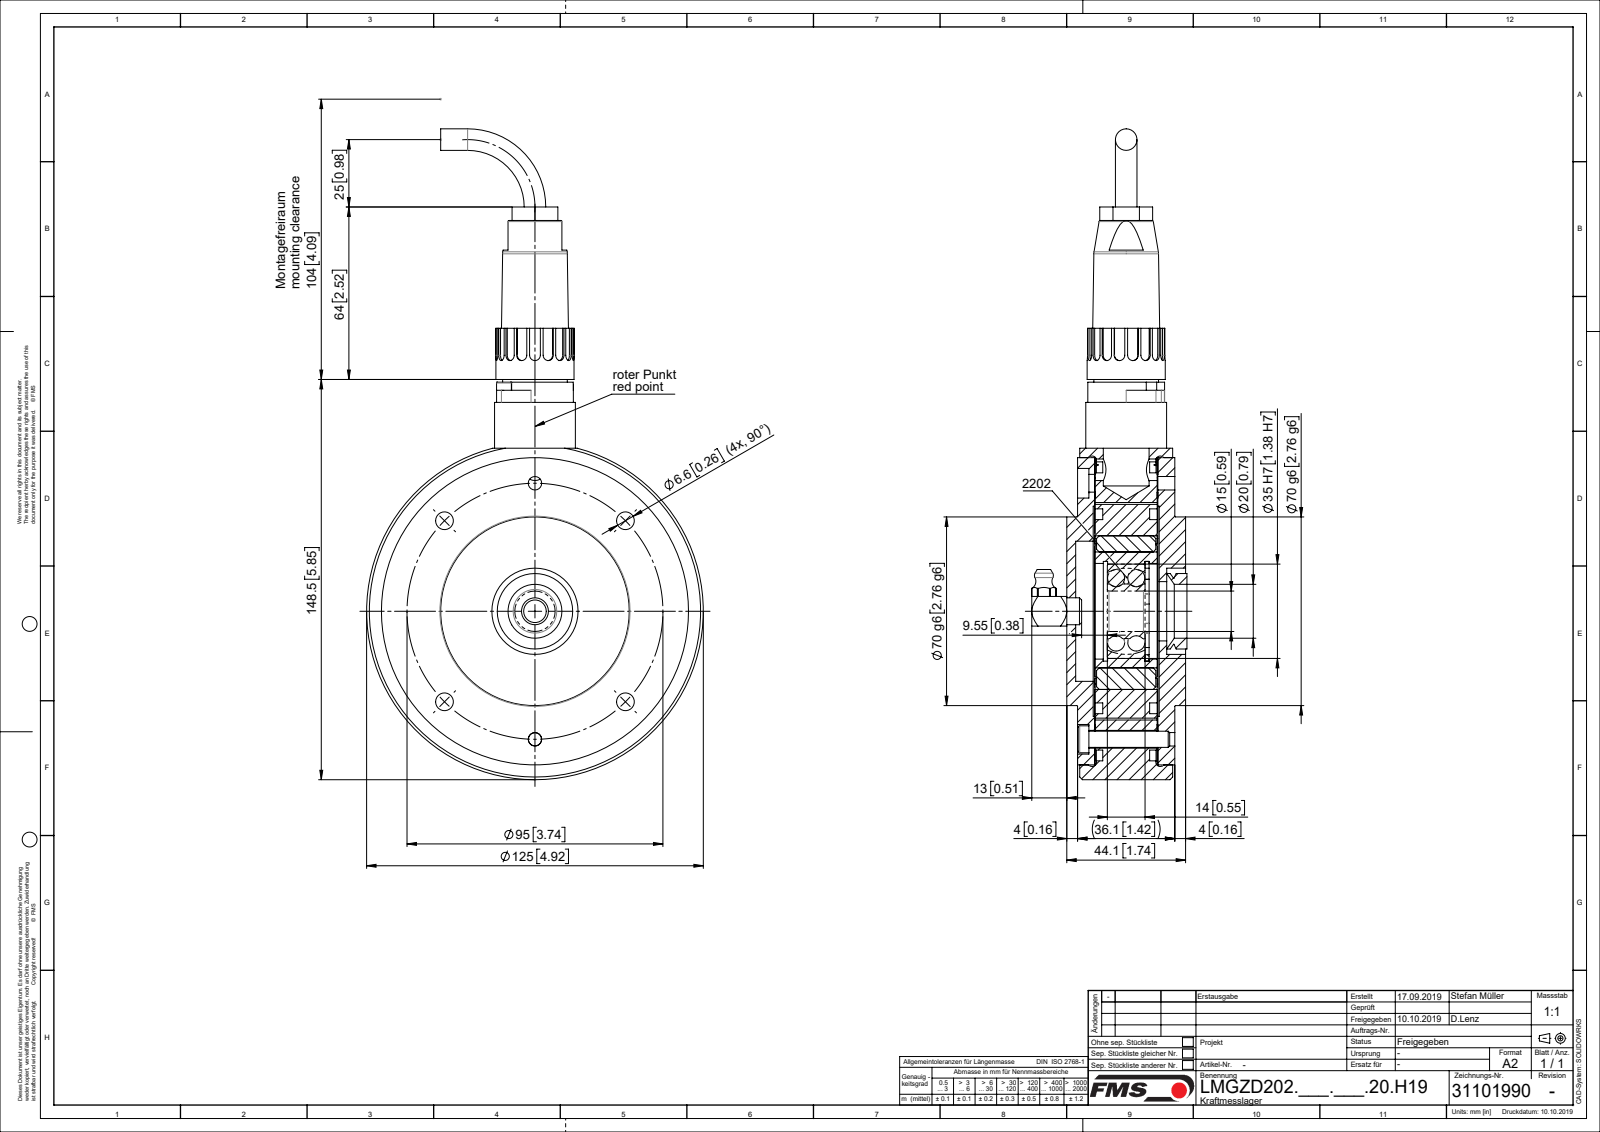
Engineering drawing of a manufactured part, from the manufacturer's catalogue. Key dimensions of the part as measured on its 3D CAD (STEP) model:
Part name (STEP PRODUCT): Flanschstecker_Kunstst_7Pol_01; 51064_01; Si-Ring DIN472_D35x1.5; 49027_01 (+8 more)
STEP written by: SolidWorks 2018 (CONFIG_CONTROL_DESIGN)
Units: millimetres
Bodies: 39 solids, 692 faces (179 planar, 377 cylindrical, 136 other)
Overall size (bounding box): 241.5 × 125 × 57.6
Volume: 462 421 mm³ · Surface area: 151 494 mm²
Round holes (diameter × count): ⌀2.5 ×6, ⌀6.6 ×6, ⌀6.8 ×4, ⌀3.4 ×2, ⌀3.6 ×2, ⌀5 ×2, ⌀8 ×2, ⌀11 ×2, ⌀22 ×2, ⌀6 ×1, ⌀9 ×1, ⌀10.5 ×1
Round bosses / shafts (diameter × count): ⌀2.15 ×7, ⌀10 ×2, ⌀5.5 ×2, ⌀3 ×2, ⌀125 ×1, ⌀114 ×1, ⌀103 ×1, ⌀70 ×1
Partial cylindrical surfaces — rounded edges, fillets, slot ends (radius × count): R2 ×17, R5 ×8, R0.1 ×4, R9 ×4, R3 ×2, R3.58 ×2, R4.5 ×1, R13.1 ×1
Main face-to-face distances: 23.25, 6.3, 6.55, 29.55, 29.8, 23, 23.5, 23.75, 4, 33.8
Hole centre spacings: 47.5, 16.26, 23, 34.67, 36.36, 67.18, 67.54, 87.77
